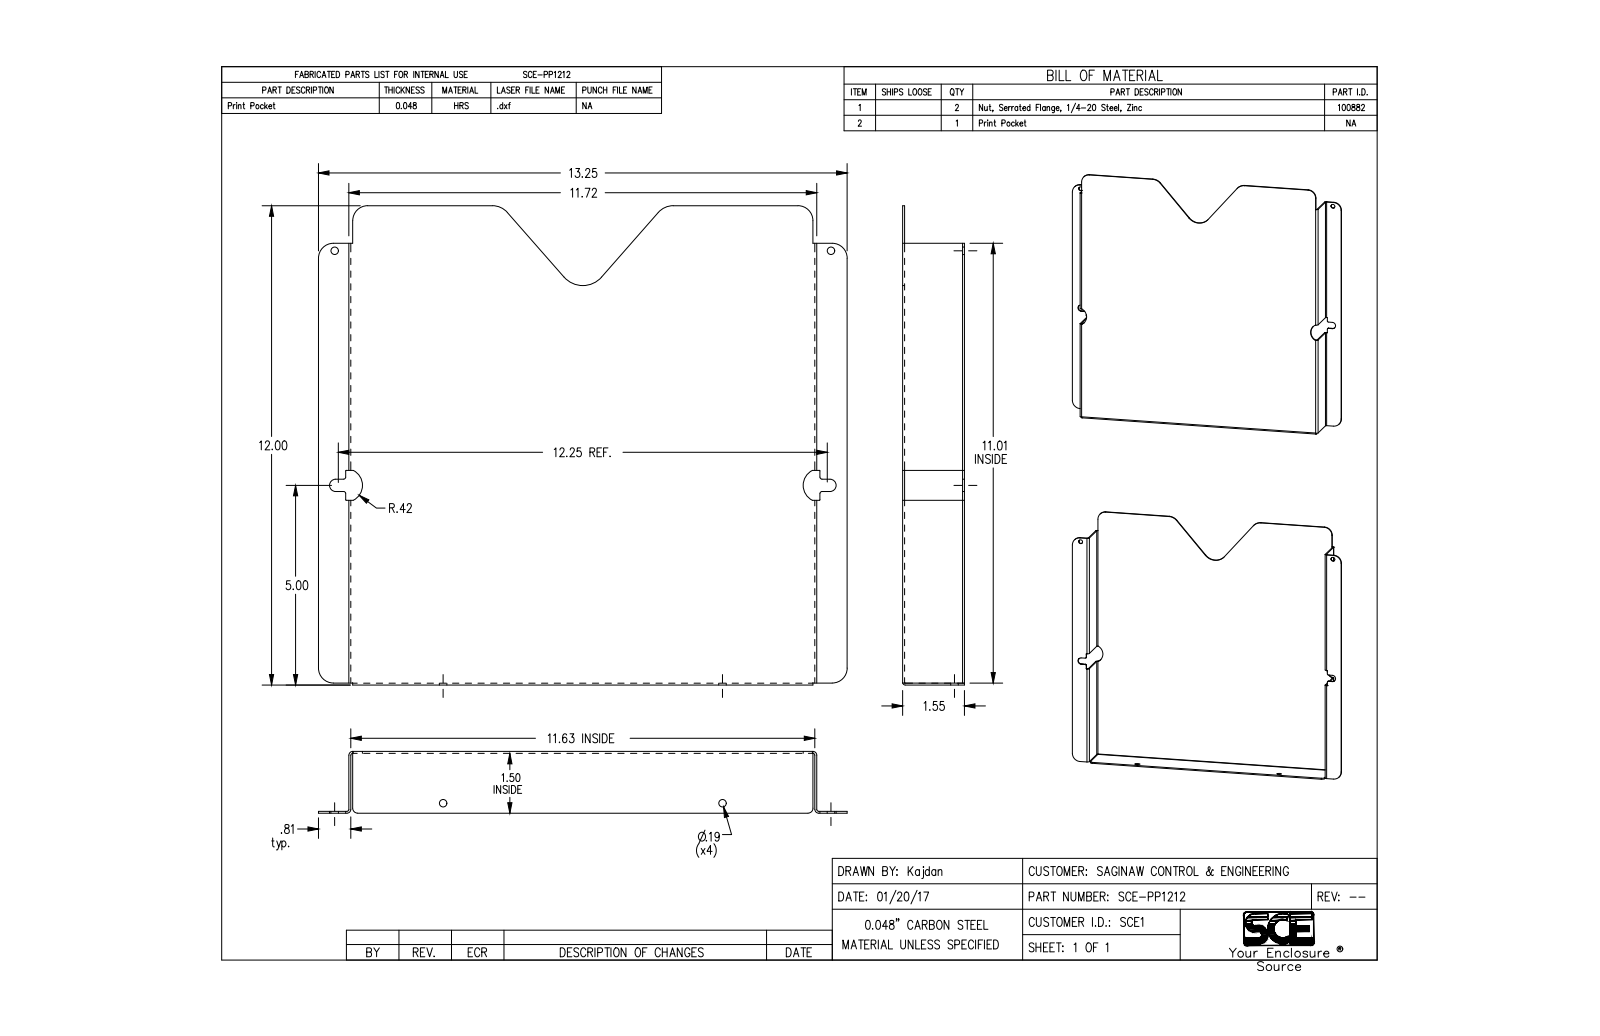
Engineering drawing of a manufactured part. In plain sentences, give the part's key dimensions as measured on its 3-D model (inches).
The part is named "SCE-PP1212". Its 3-D file was written by "SolidWorks 2019 (CONFIG_CONTROL_DESIGN)". It is 5 solids with 566 faces: 197 planar, 63 cylindrical and 306 other. Overall it measures 13.245 by 12.001 by 1.548 inches. Its volume is 9.607 cubic inches and its surface area 402.5 square inches. Round holes: 4 of diameter 0.188, 2 of diameter 0.25. Round bosses or shafts: 2 of diameter 0.563, 2 of diameter 0.248. Partial cylindrical surfaces (rounded edges, fillets, slot ends): 12 of radius 0.029, 6 of radius 0.375, 4 of radius 0.015, 4 of radius 0.05, 2 of radius 0.046, 2 of radius 0.047, 2 of radius 0.094, 2 of radius 0.095. The main face-to-face distances are 0.048, 1.5, 1.548, 1.452, 11.673, 11.625, 11.721, 11.673, 0.048, 0.81. The hole center spacings are 5.874, 7, 12.25, 12.433, 13.668, 13.668.
